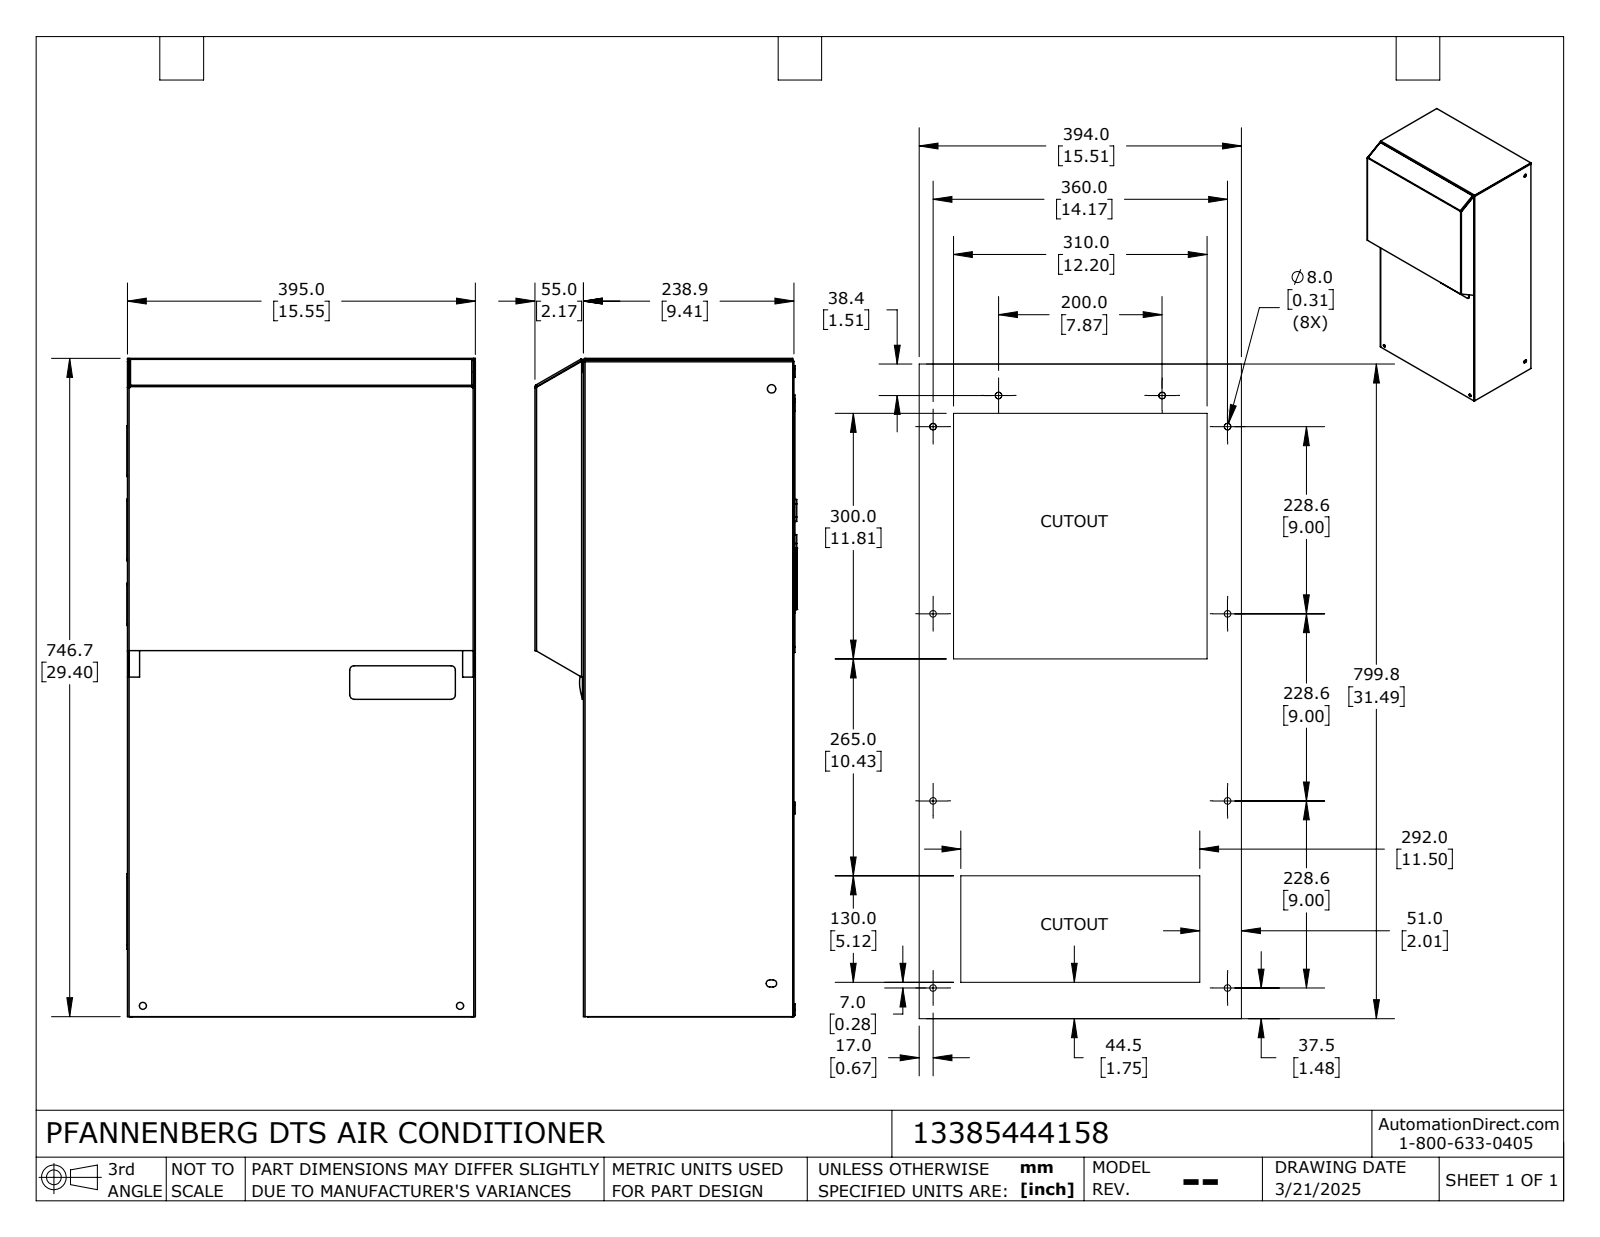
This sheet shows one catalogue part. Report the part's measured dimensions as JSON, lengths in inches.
{"part_name": "13385444158_Default", "step_written_by": "SolidWorks 2024 (CONFIG_CONTROL_DESIGN)", "units": "inches", "bodies": {"solids": 1, "faces": 1711, "planar": 962, "cylindrical": 722, "other": 27}, "overall_size": [29.397, 15.571, 11.698], "volume_in3": 4278, "surface_area_in2": 4492, "round_holes": [[0.165, 19], [0.283, 10], [0.163, 8], [0.157, 6], [0.197, 4], [0.236, 2], [0.315, 2], [0.437, 2], [0.118, 1], [0.318, 1], [0.375, 1], [0.825, 1]], "round_bosses_or_shafts": [[0.512, 10]], "partial_cylinders_radius": [[0.125, 140], [0.112, 129], [0.031, 12], [0.079, 12], [0.197, 12], [0.079, 11], [0.113, 11], [0.198, 10]], "face_to_face_distances": [0.048, 0.03, 0.078, 9.278, 9.307, 9.355, 0.05, 9.327, 9.357, 9.405], "hole_center_spacings": [28.674, 1.07, 1.134, 1.713, 3.937, 7.887, 8.938, 9.012]}
